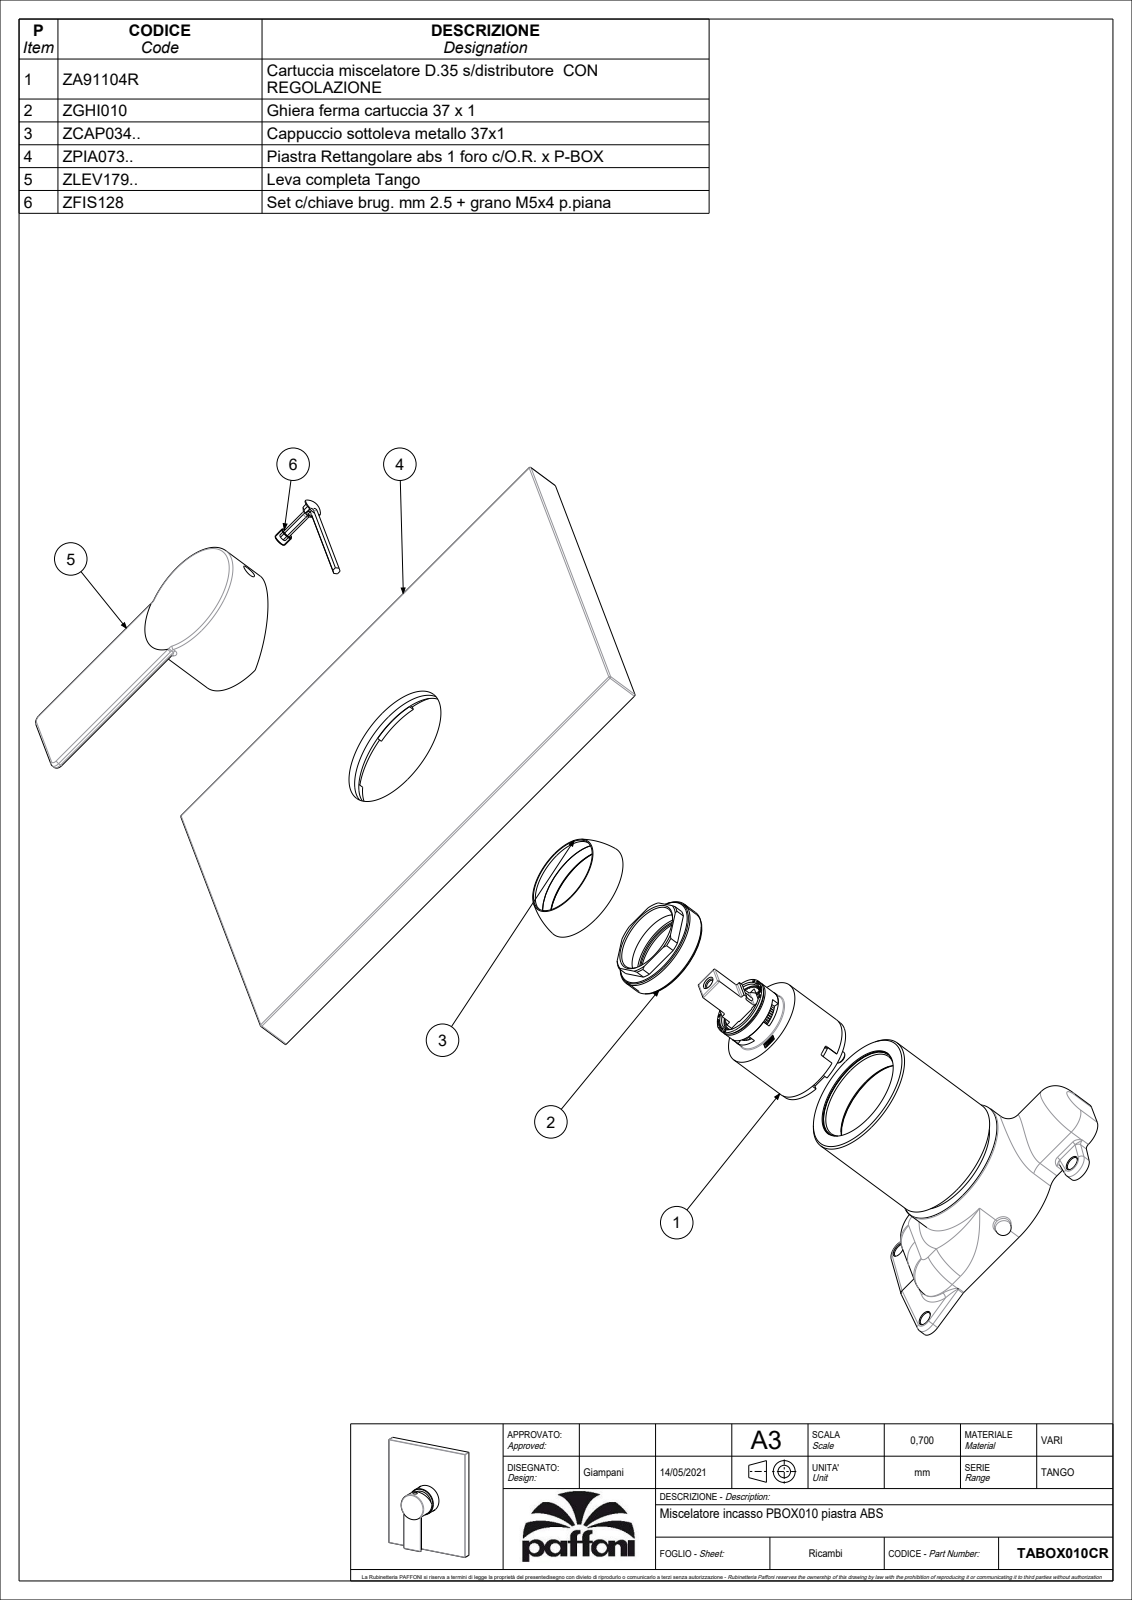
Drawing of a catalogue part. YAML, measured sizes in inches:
part_name: "TABOX010CR"
step_written_by: "CREO PARAMETRIC BY PTC INC, 2020044 (CONFIG_CONTROL_DESIGN)"
units: inches
bodies: {solids: 2, faces: 159, planar: 51, cylindrical: 53, other: 55}
overall_size: [7.559, 6.063, 2.583]
volume: 26.58
surface_area: 143
round_holes:
  - {diameter: 0.118, count: 1}
  - {diameter: 0.165, count: 1}
  - {diameter: 0.217, count: 1}
  - {diameter: 1.205, count: 1}
  - {diameter: 1.417, count: 1}
  - {diameter: 1.476, count: 1}
round_bosses_or_shafts:
  - {diameter: 1.894, count: 1}
  - {diameter: 1.791, count: 1}
  - {diameter: 0.299, count: 1}
partial_cylinders:
  - {radius: 0.02, count: 10}
  - {radius: 0.039, count: 6}
  - {radius: 0.059, count: 4}
  - {radius: 0.118, count: 2}
  - {radius: 0.138, count: 1}
face_to_face_distances: [0.531, 6.063, 7.559, 2.563, 2.031, 0.118, 2.445, 1.913, 0.138, 0.02]
